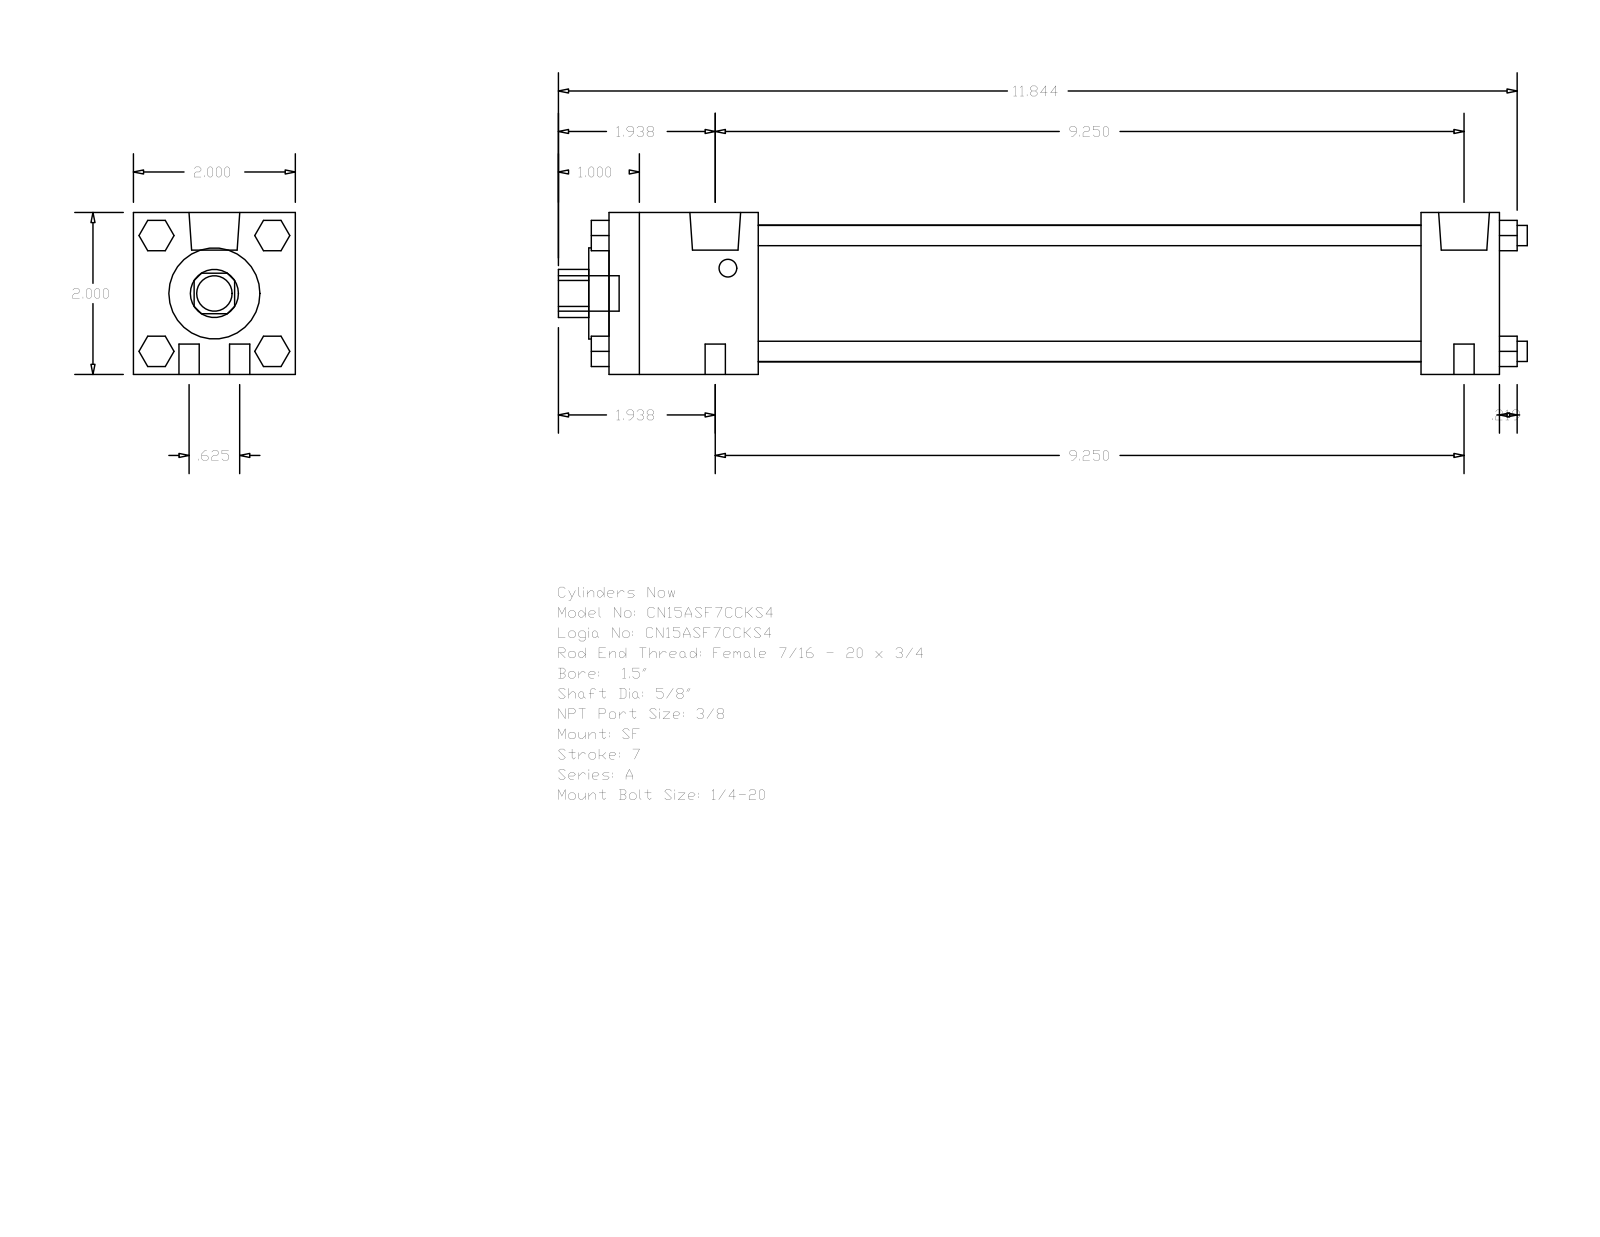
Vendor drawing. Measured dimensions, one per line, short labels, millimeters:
name: A_SF__0150_0.625
written by: GSSL Pune (CONFIG_CONTROL_DESIGN)
unit: mm
bodies: 0 solids, 124 faces (94 planar, 30 cylindrical, 0 other)
size: 304.01 × 50.8 × 50.8
holes: 1× ⌀15.88, 1× ⌀28.57, 1× ⌀42.93
bosses: 8× ⌀6.35, 2× ⌀15.93, 2× ⌀5.56, 1× ⌀11.11
rounds: 1× R7.54
face distances: 50.8, 279.39, 46.83, 254.79, 207.96, 232.56, 24.6, 9.52, 6.35, 53.18
